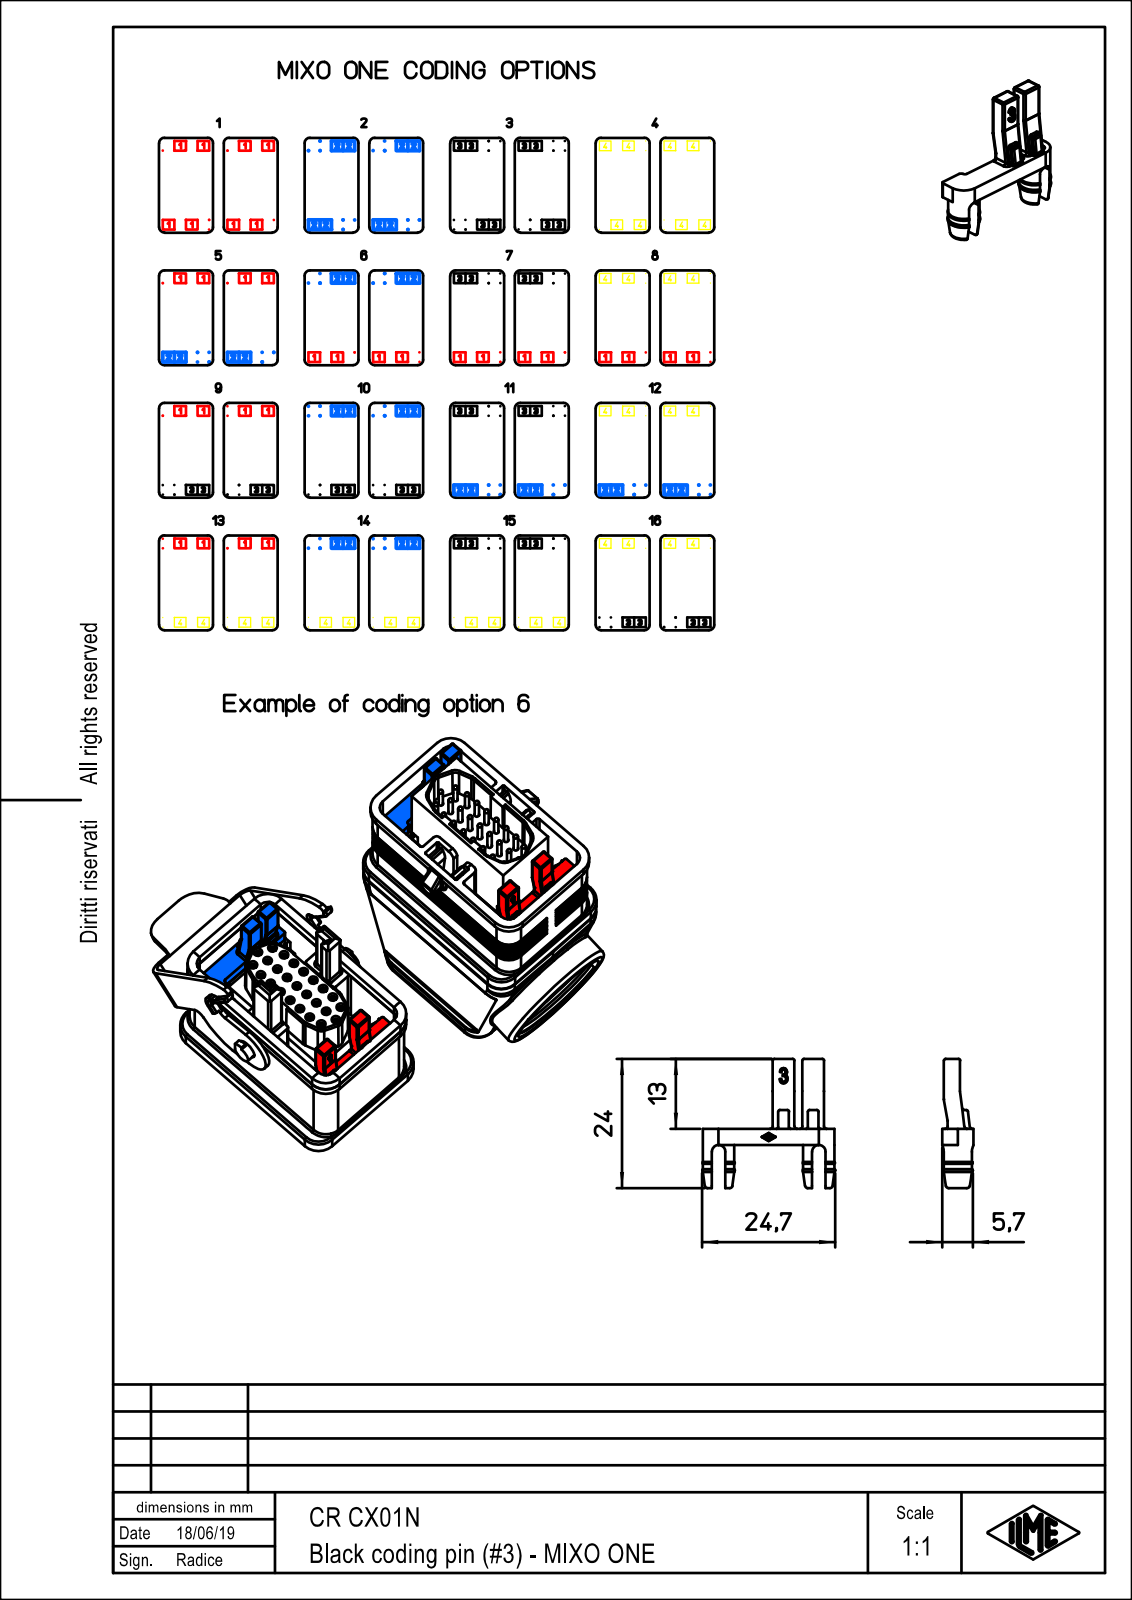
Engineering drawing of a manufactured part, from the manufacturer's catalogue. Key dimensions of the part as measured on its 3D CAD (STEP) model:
Part name (STEP PRODUCT): CR_CX01N
STEP written by: Creo Elements/Direct Modeling 20.1B 02-Apr-2019 (C) Parametric Technology GmbH (AUTOMOTIVE_DESIGN)
Units: millimetres
Bodies: 1 solid, 49 faces (35 planar, 10 cylindrical, 4 other)
Overall size (bounding box): 24.4 × 24 × 5.8
Volume: 878 mm³ · Surface area: 1 139 mm²
Round bosses / shafts (diameter × count): ⌀5.8 ×2
Partial cylindrical surfaces — rounded edges, fillets, slot ends (radius × count): R1.25 ×2
Main face-to-face distances: 5.5, 3, 2.5, 4, 18.6, 5.8, 3.3, 0.7, 4.8, 2.3
